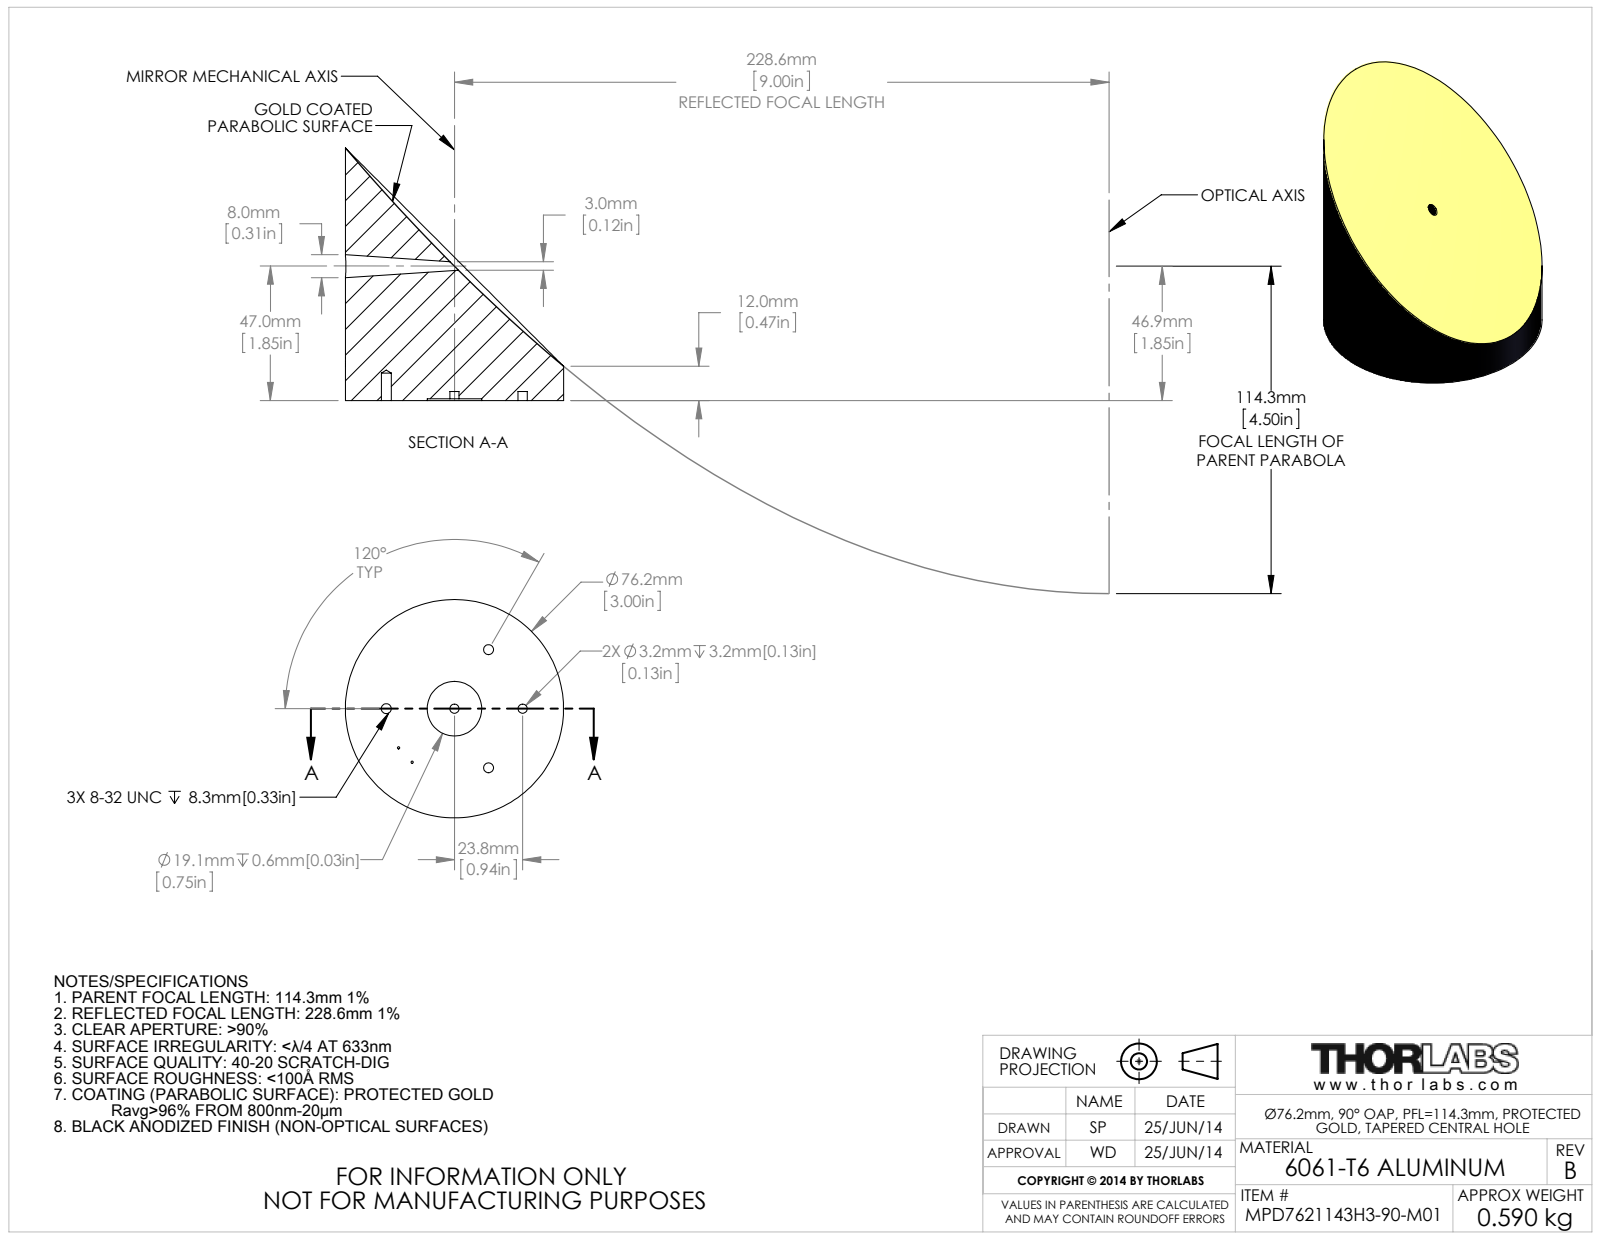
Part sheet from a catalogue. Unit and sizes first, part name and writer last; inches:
Units: inches
Overall size (bounding box): 3.473 × 3 × 3
Round holes (diameter × count): ⌀0.136 ×3, ⌀0.126 ×2, ⌀0.75 ×1
Round bosses / shafts (diameter × count): ⌀3 ×1
Main face-to-face distances: 0.025, 0.125, 0.1
Hole centre spacings: 0.937, 0.938, 1.624, 1.624, 1.875
Volume: 13.41 in³ · Surface area: 37.24 in²
Bodies: 1 solid, 71 faces (4 planar, 53 cylindrical, 14 other)
Part name (STEP PRODUCT): 24804-E0W
STEP written by: SolidWorks 2014 (CONFIG_CONTROL_DESIGN)
